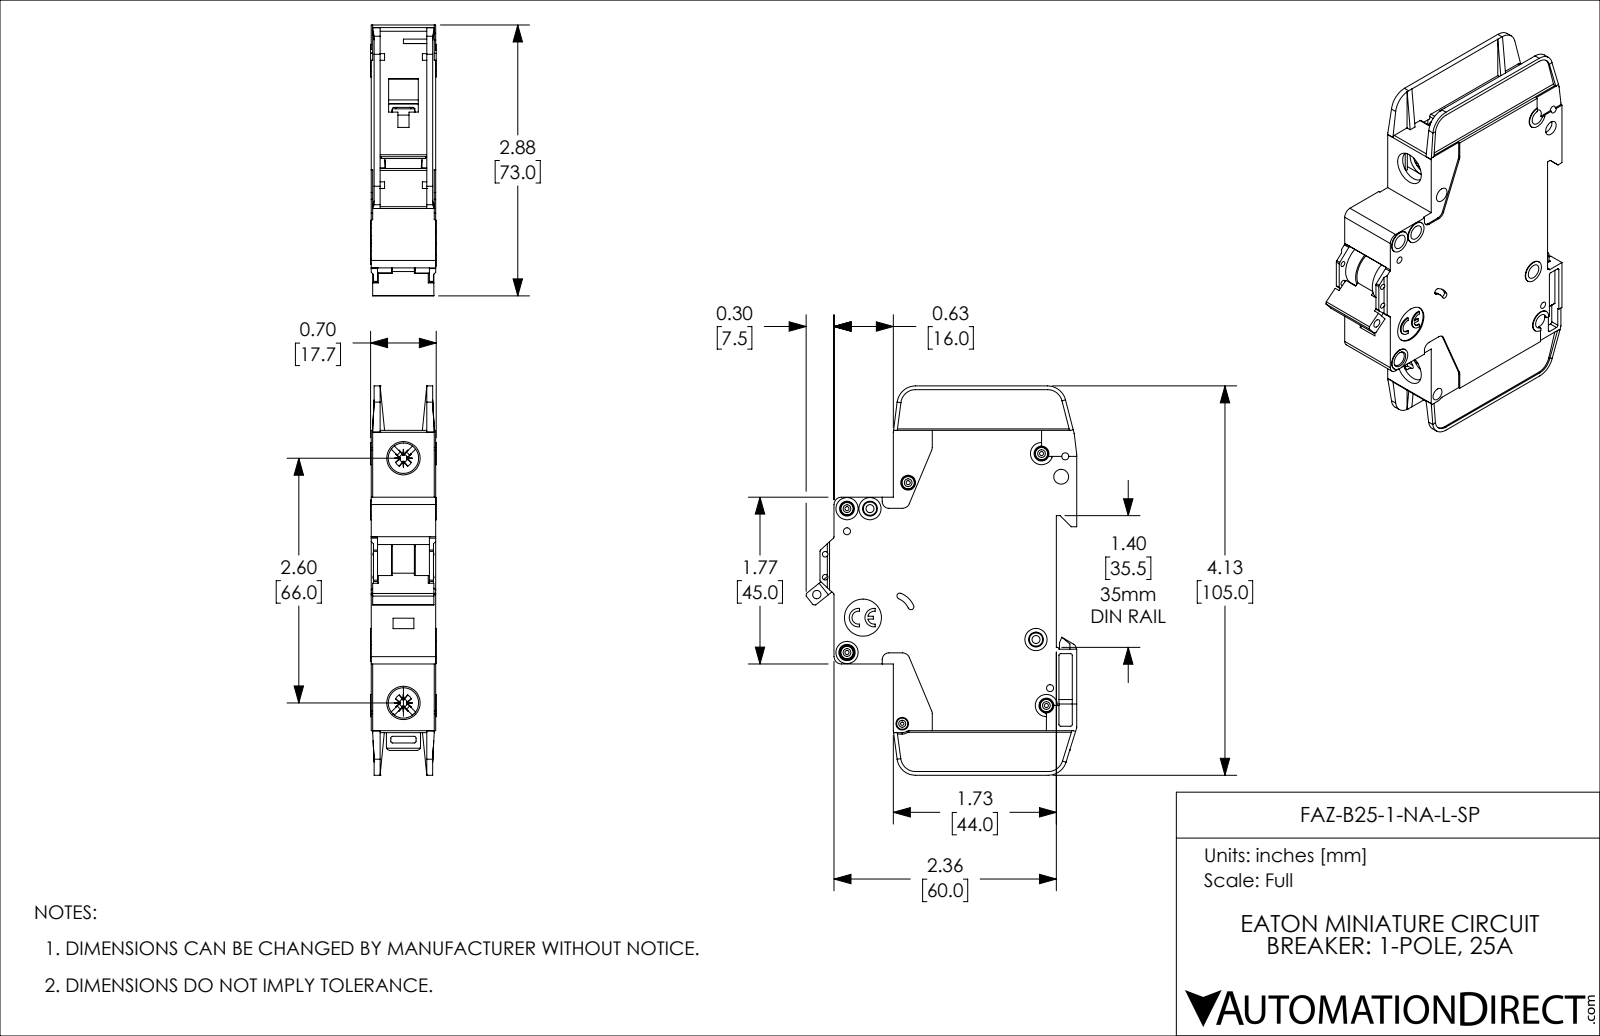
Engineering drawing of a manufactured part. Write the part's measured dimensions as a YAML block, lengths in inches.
part_name: "FAZ-B25-1-NA-L-SP"
step_written_by: "SolidWorks 2019 (AUTOMOTIVE_DESIGN)"
units: inches
bodies: {solids: 1, faces: 1127, planar: 671, cylindrical: 357, other: 99}
overall_size: [4.134, 2.876, 0.697]
volume: 4.682
surface_area: 41.01
round_holes:
  - {diameter: 0.157, count: 8}
  - {diameter: 0.043, count: 5}
  - {diameter: 0.075, count: 4}
  - {diameter: 0.059, count: 2}
  - {diameter: 0.085, count: 2}
  - {diameter: 0.323, count: 2}
  - {diameter: 0.035, count: 1}
  - {diameter: 0.089, count: 1}
  - {diameter: 0.098, count: 1}
  - {diameter: 0.134, count: 1}
  - {diameter: 0.394, count: 1}
round_bosses_or_shafts:
  - {diameter: 0.13, count: 5}
  - {diameter: 0.236, count: 4}
  - {diameter: 0.118, count: 2}
  - {diameter: 0.098, count: 1}
partial_cylinders:
  - {radius: 0.02, count: 42}
  - {radius: 0.016, count: 10}
  - {radius: 0.039, count: 10}
  - {radius: 0.079, count: 8}
  - {radius: 0.197, count: 5}
  - {radius: 0.008, count: 4}
  - {radius: 0.026, count: 4}
  - {radius: 0.043, count: 4}
face_to_face_distances: [0.047, 0.685, 0.591, 0.638, 0.094, 0.543, 0.016, 0.031, 0.496, 0.575]
hole_center_spacings: [0.244, 0.537, 0.87, 0.189, 0.199, 0.204, 0.221, 0.24]
